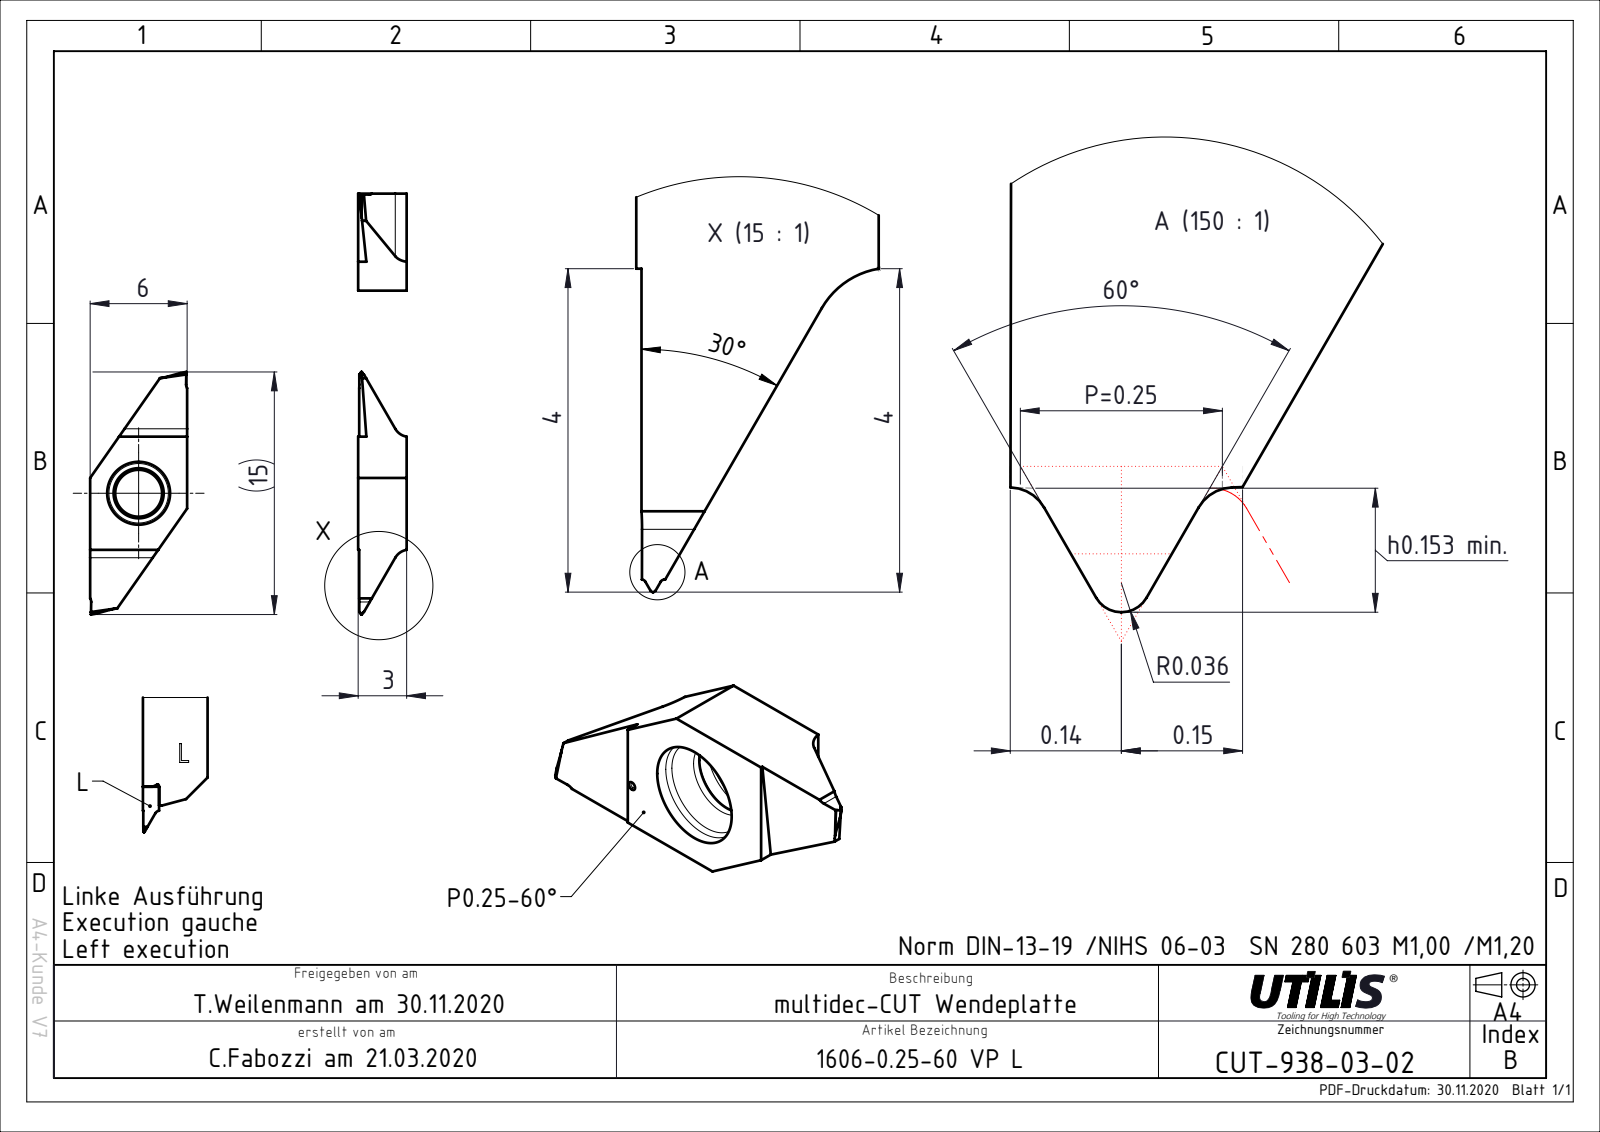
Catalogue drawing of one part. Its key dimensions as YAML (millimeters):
part_name: "CUT-938-03; ASME Y14.5"
step_written_by: "FormatWorks Professional (AP242_MANAGED_MODEL_BASED_3D_ENGINEERING_MIM_LF)"
units: millimeters
bodies: {solids: 1, faces: 40, planar: 22, cylindrical: 14, other: 4}
overall_size: [15, 6, 3]
volume: 127
surface_area: 210
round_holes:
  - {diameter: 2.9, count: 1}
partial_cylinders:
  - {radius: 1, count: 2}
face_to_face_distances: [6, 3, 9, 12, 7, 11.14, 13.21, 13.22]
